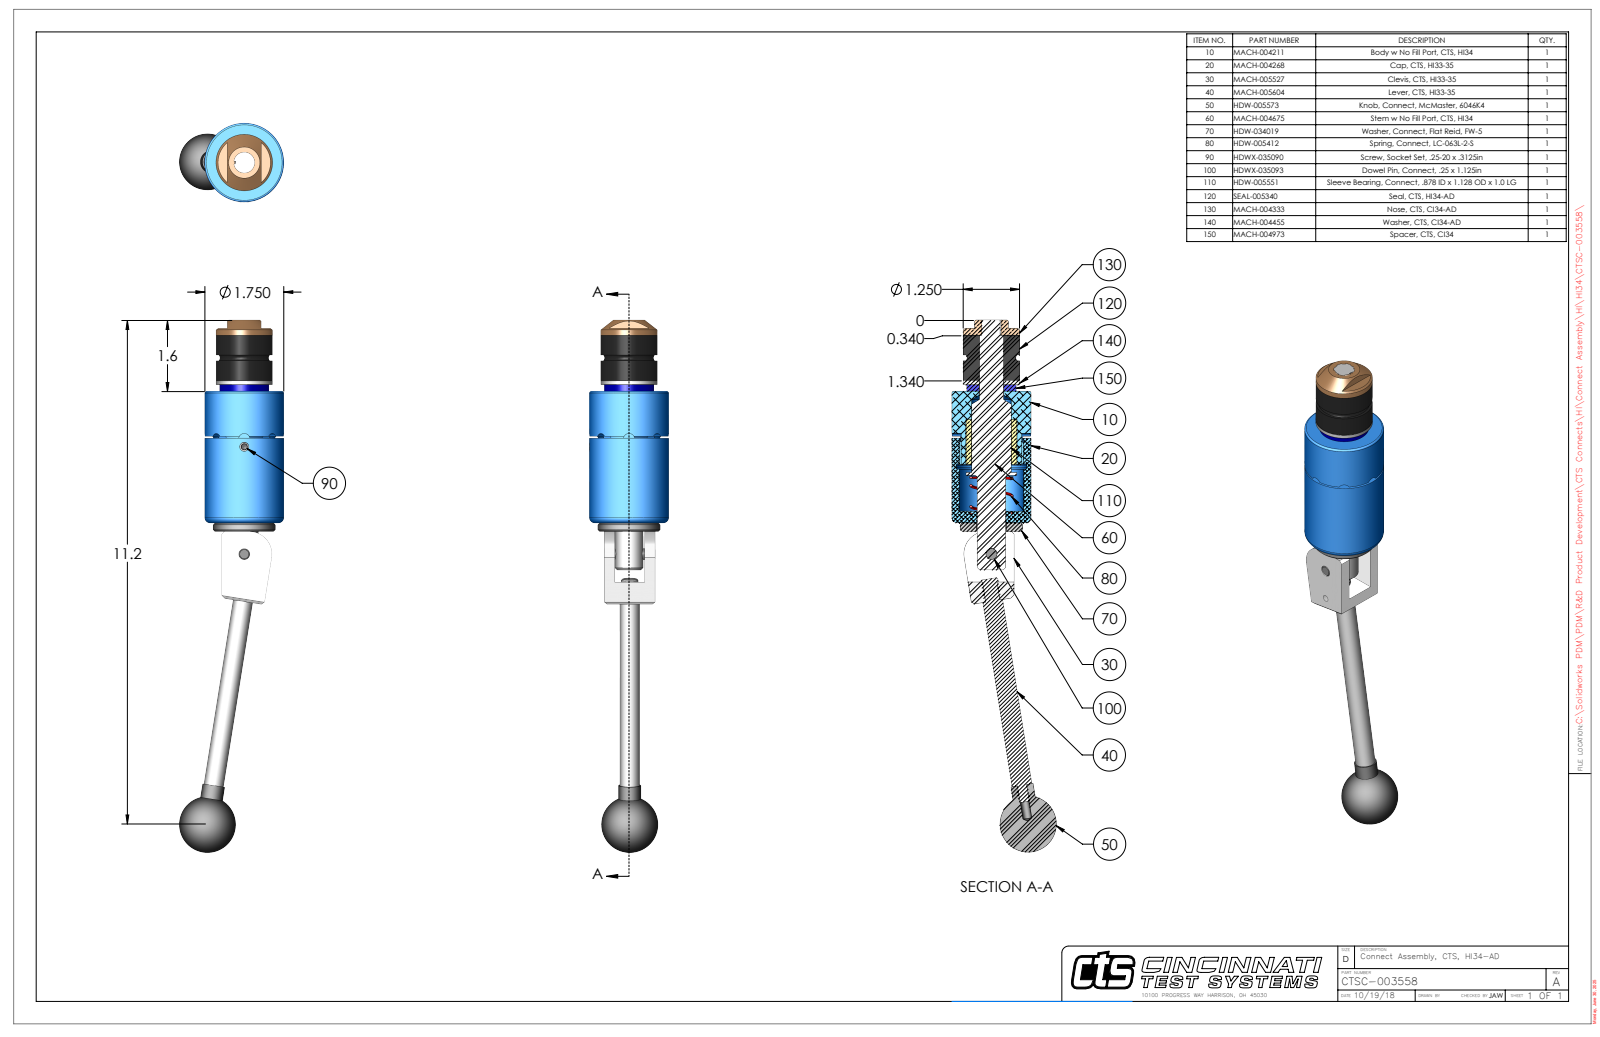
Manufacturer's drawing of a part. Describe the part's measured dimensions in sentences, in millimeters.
The part is named "CTSC-003558". Its 3-D file was written by "SolidWorks 2023 (AUTOMOTIVE_DESIGN)". It is 10 solids with 238 faces: 77 planar, 102 cylindrical and 59 other. Overall it measures 299.5 by 58.7 by 44.5 millimeters. Its volume is 195 500 cubic millimeters and its surface area 45 860 square millimeters. Round holes: 2 of diameter 5.1, 1 of diameter 3.8, 1 of diameter 6.3, 1 of diameter 6.4, 1 of diameter 8, 1 of diameter 10.7, 1 of diameter 13.5, 1 of diameter 13.7, 1 of diameter 13.9, 1 of diameter 13.9, 1 of diameter 16.1, 1 of diameter 16.7. Round bosses or shafts: 2 of diameter 12.7, 2 of diameter 11.2, 2 of diameter 6.4, 1 of diameter 44.5, 1 of diameter 35.1, 1 of diameter 31.8, 1 of diameter 27.7, 1 of diameter 15.9. Partial cylindrical surfaces (rounded edges, fillets, slot ends): 4 of radius 3.2, 2 of radius 0.7, 1 of radius 12.7, 1 of radius 17.7, 1 of radius 21. The main face-to-face distances are 31.4, 25.4, 74.1, 105.5, 6, 80.1, 27.8, 2.4, 3.6, 77.7. The hole center spacings are 18.8, 60.4, 79.1.
